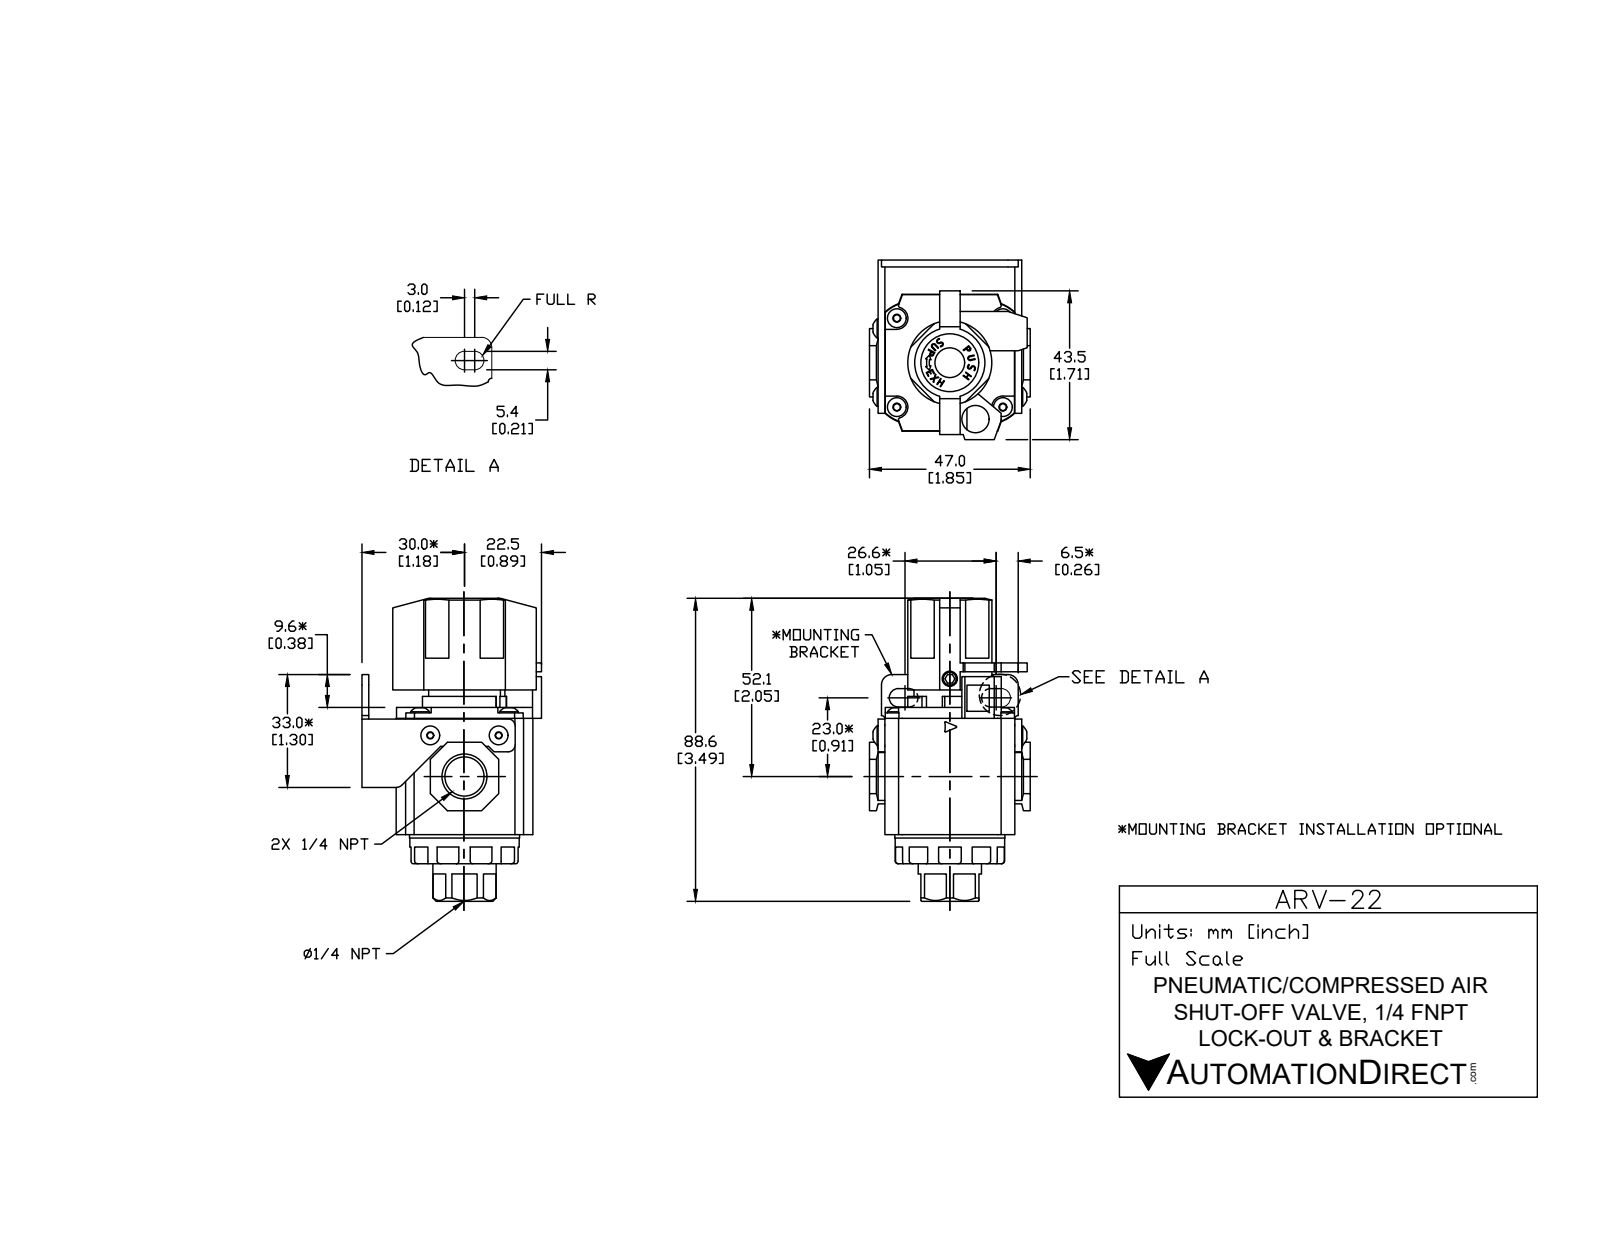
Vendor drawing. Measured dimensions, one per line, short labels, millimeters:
name: ARV-22
written by: SolidWorks 2015 (CONFIG_CONTROL_DESIGN)
unit: mm
bodies: 18 solids, 396 faces (284 planar, 75 cylindrical, 37 other)
size: 89 × 52.6 × 47
volume: 84 804 mm³; area: 28 884 mm²
holes: 1× ⌀8, 1× ⌀11.13, 1× ⌀17.22
bosses: 4× ⌀5.5, 1× ⌀31.5, 1× ⌀30.87, 1× ⌀24.6, 1× ⌀18.7, 1× ⌀12.3
rounds: 6× R1.5, 4× R2.7, 4× R3.85, 2× R1, 2× R2, 2× R3, 1× R5, 1× R9.18
face distances: 2, 40, 34, 37.2, 3.2, 38, 10, 17, 8, 50
hole spacings: 18.12
